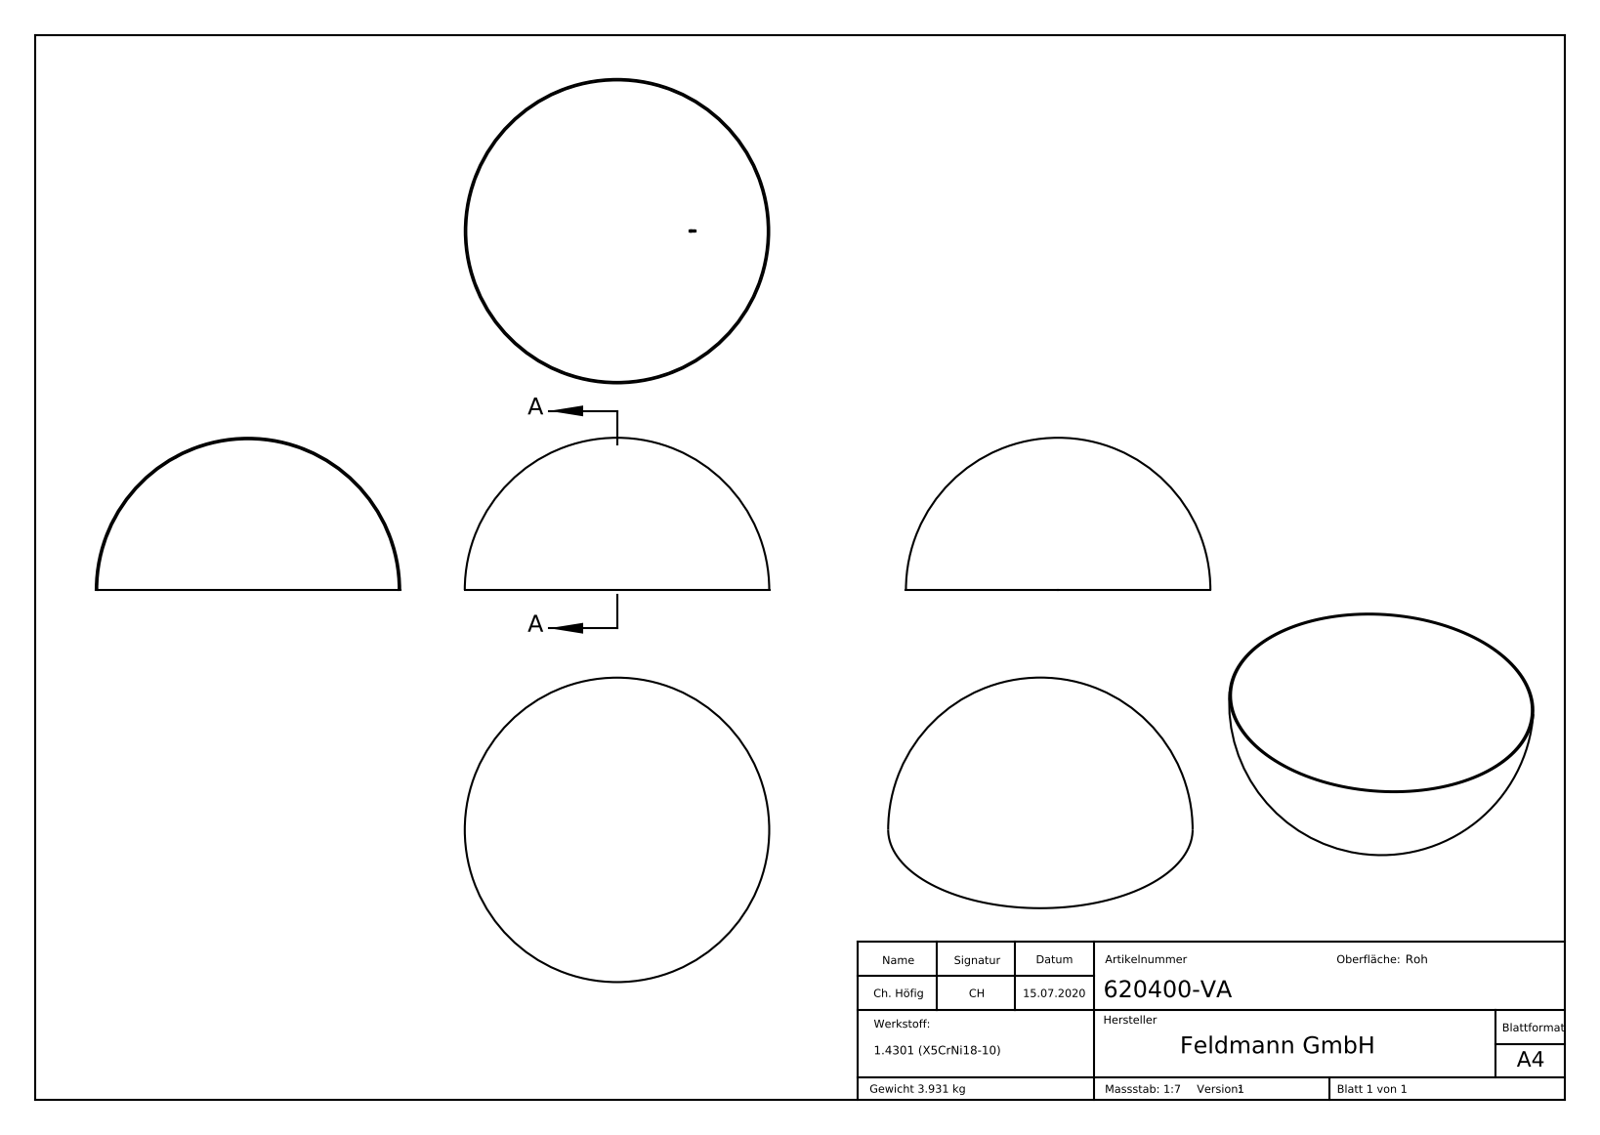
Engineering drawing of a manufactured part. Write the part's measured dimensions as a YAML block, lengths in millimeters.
part_name: "620400-VA"
step_written_by: "SolidWorks 2018 (CONFIG_CONTROL_DESIGN)"
units: millimeters
bodies: {solids: 1, faces: 217, planar: 99, cylindrical: 0, other: 118}
overall_size: [400, 400, 200]
volume: 497645
surface_area: 500159
face_to_face_distances: [0.45, 2.65, 2.54, 0.61, 1.19, 3.88, 0.53, 5.19, 0.55, 0.81]
